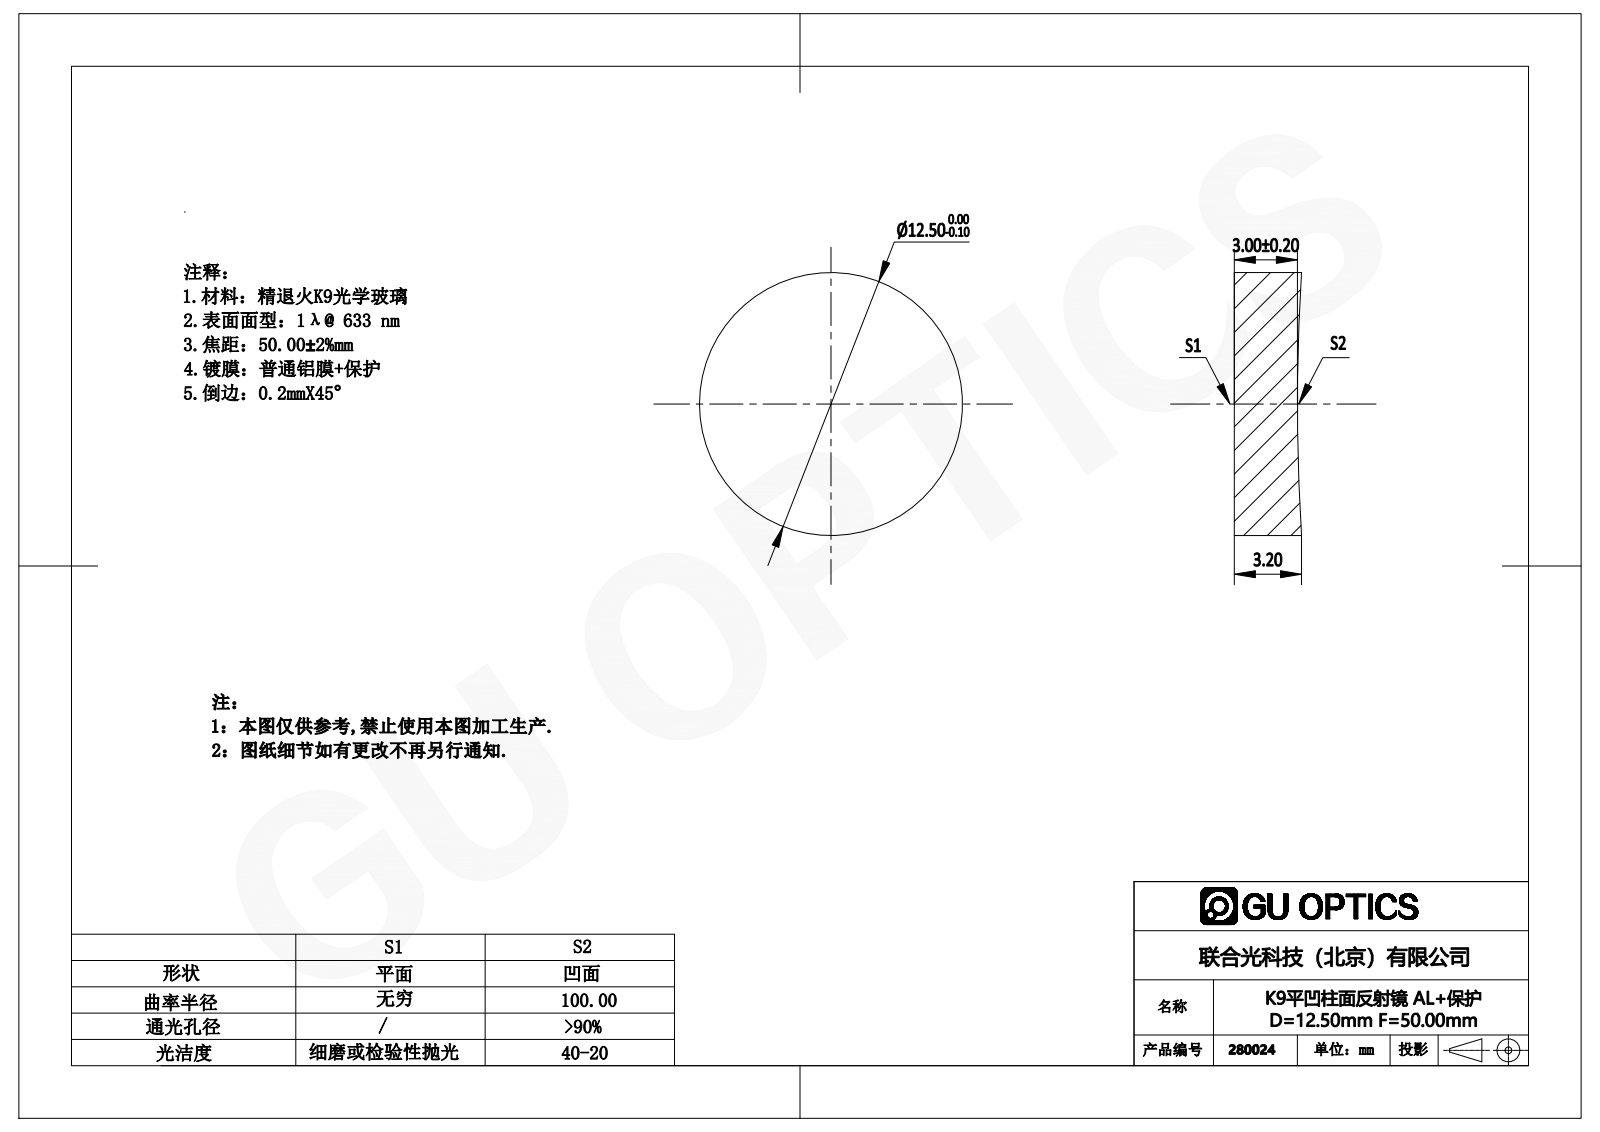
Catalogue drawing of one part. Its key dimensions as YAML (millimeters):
part_name: "280002"
step_written_by: "SolidWorks 2020 (CONFIG_CONTROL_DESIGN)"
units: millimeters
bodies: {solids: 1, faces: 3, planar: 1, cylindrical: 2, other: 0}
overall_size: [12.5, 12.5, 3.2]
volume: 374
surface_area: 367
round_bosses_or_shafts:
  - {diameter: 12.5, count: 1}
partial_cylinders:
  - {radius: 100, count: 1}
